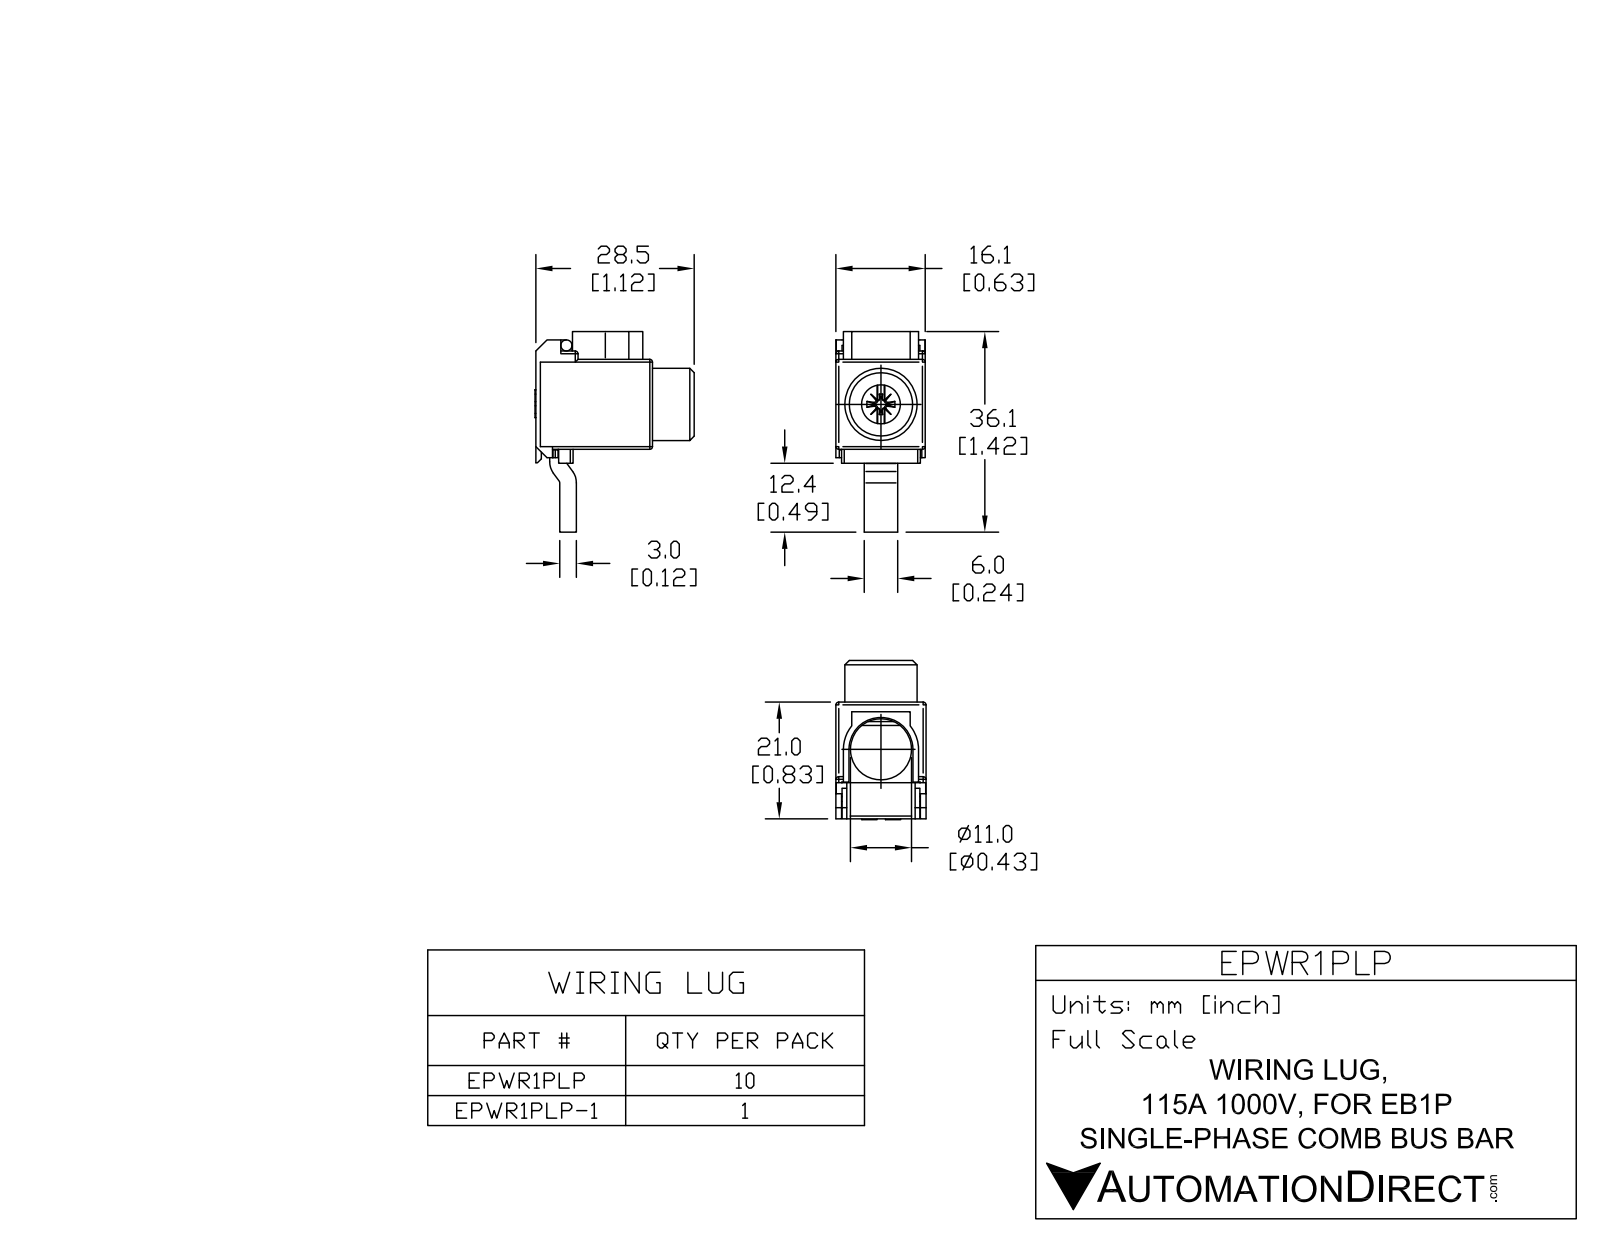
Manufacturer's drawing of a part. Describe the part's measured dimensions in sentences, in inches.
The part is named "EPWR1PLP". Its 3-D file was written by "SolidWorks 2011 (AUTOMOTIVE_DESIGN)". It is 1 solid with 85 faces: 69 planar, 13 cylindrical and 3 other. Overall it measures 1.415 by 1.125 by 0.635 inches. Its volume is 0.35 cubic inches and its surface area 5.683 square inches. Round holes: 1 of diameter 0.275, 1 of diameter 0.445. Round bosses or shafts: 1 of diameter 0.51. Partial cylindrical surfaces (rounded edges, fillets, slot ends): 2 of radius 0.2, 1 of radius 0.188, 1 of radius 0.225, 1 of radius 0.265. The main face-to-face distances are 0.635, 0.08, 0.555, 0.835, 0.04, 0.19, 0.27, 0.565, 0.197, 0.437.
